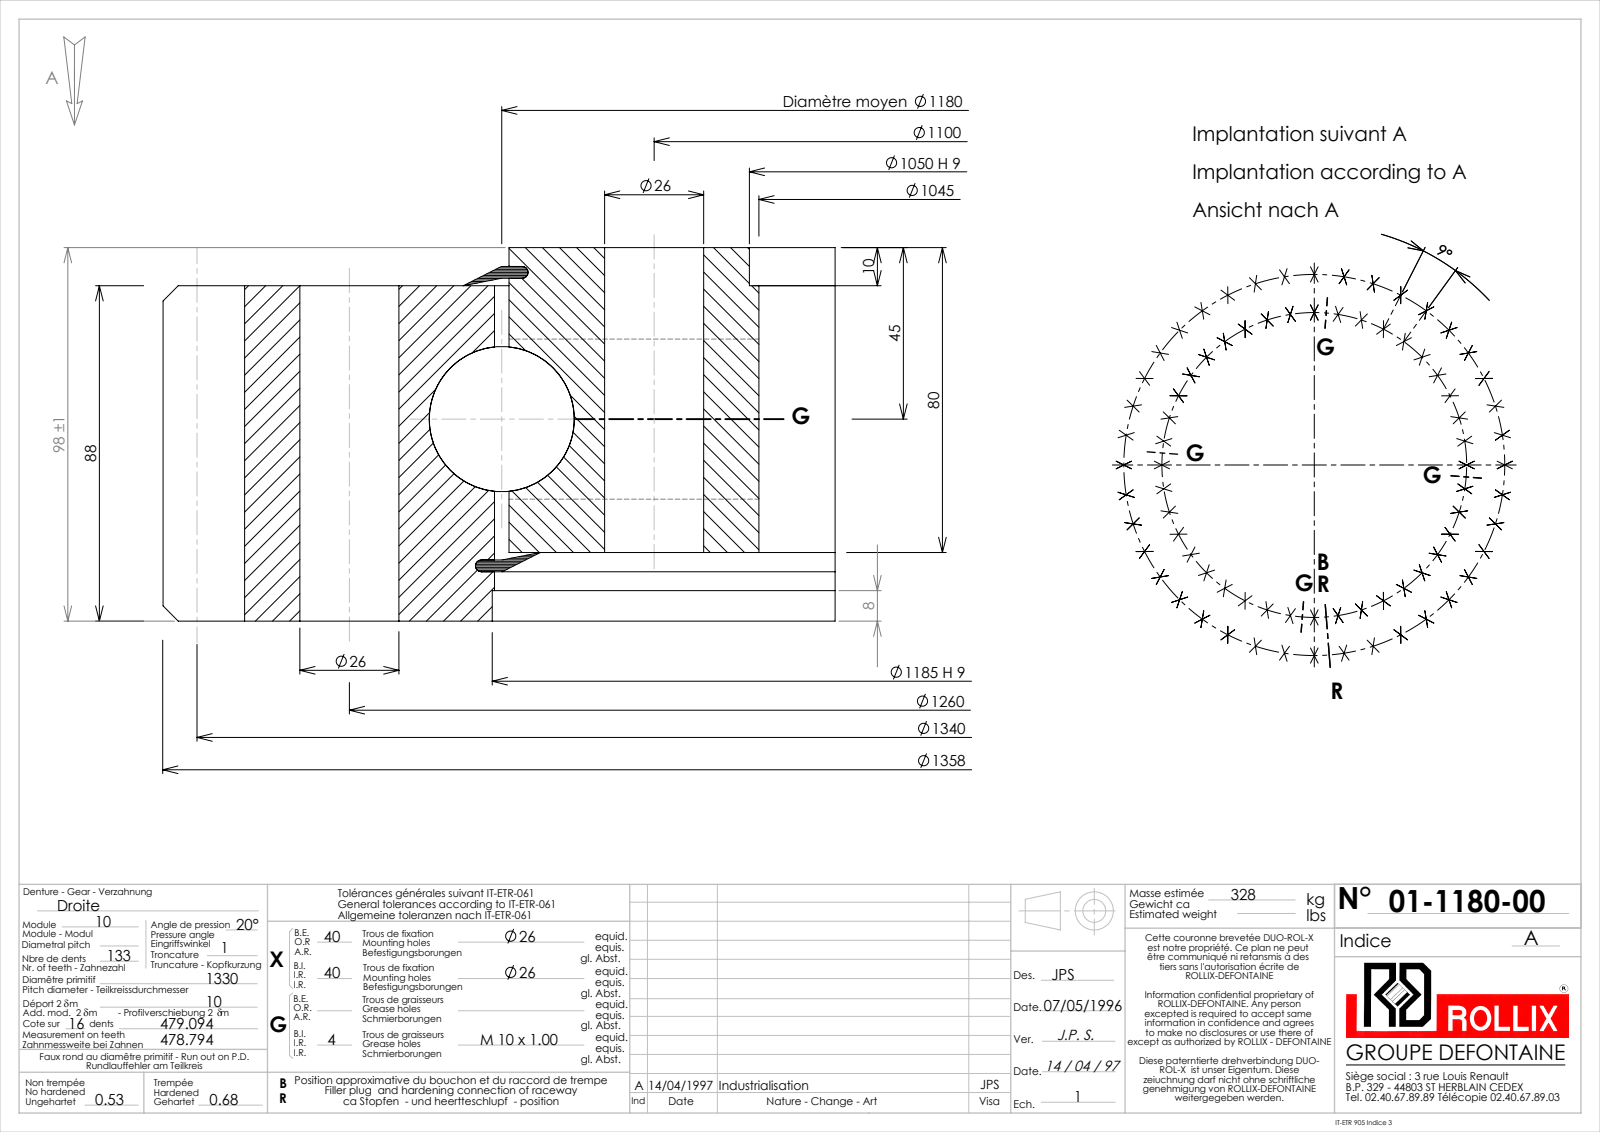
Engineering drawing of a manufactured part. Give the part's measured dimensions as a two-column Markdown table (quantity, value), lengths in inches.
| quantity | value |
| --- | --- |
| part name | 01-1180-00 |
| STEP written by | SolidWorks 2016 (CONFIG_CONTROL_DESIGN) |
| units | inches |
| bodies | 5 solids, 1028 faces (280 planar, 453 cylindrical, 295 other) |
| overall size | 53.464 × 53.461 × 3.858 |
| volume | 2 322 in³ |
| surface area | 5 611 in² |
| round holes (diameter × count) | 1.024 × 80, 0.354 × 4, 41.142 × 1, 41.339 × 1, 46.607 × 1, 46.654 × 1 |
| round bosses / shafts (diameter × count) | 46.307 × 1 |
| partial cylindrical surfaces (radius × count) | 25.886 × 1, 26.732 × 1 |
| main face-to-face distances | 3.465, 0.709, 2.756, 0.394, 3.15, 3.858, 0.077, 2.833, 0.122, 0.199 |
| hole center spacings | 3.892, 11.58, 7.76, 18.983, 32.217, 15.329, 29.158, 37.721 |
